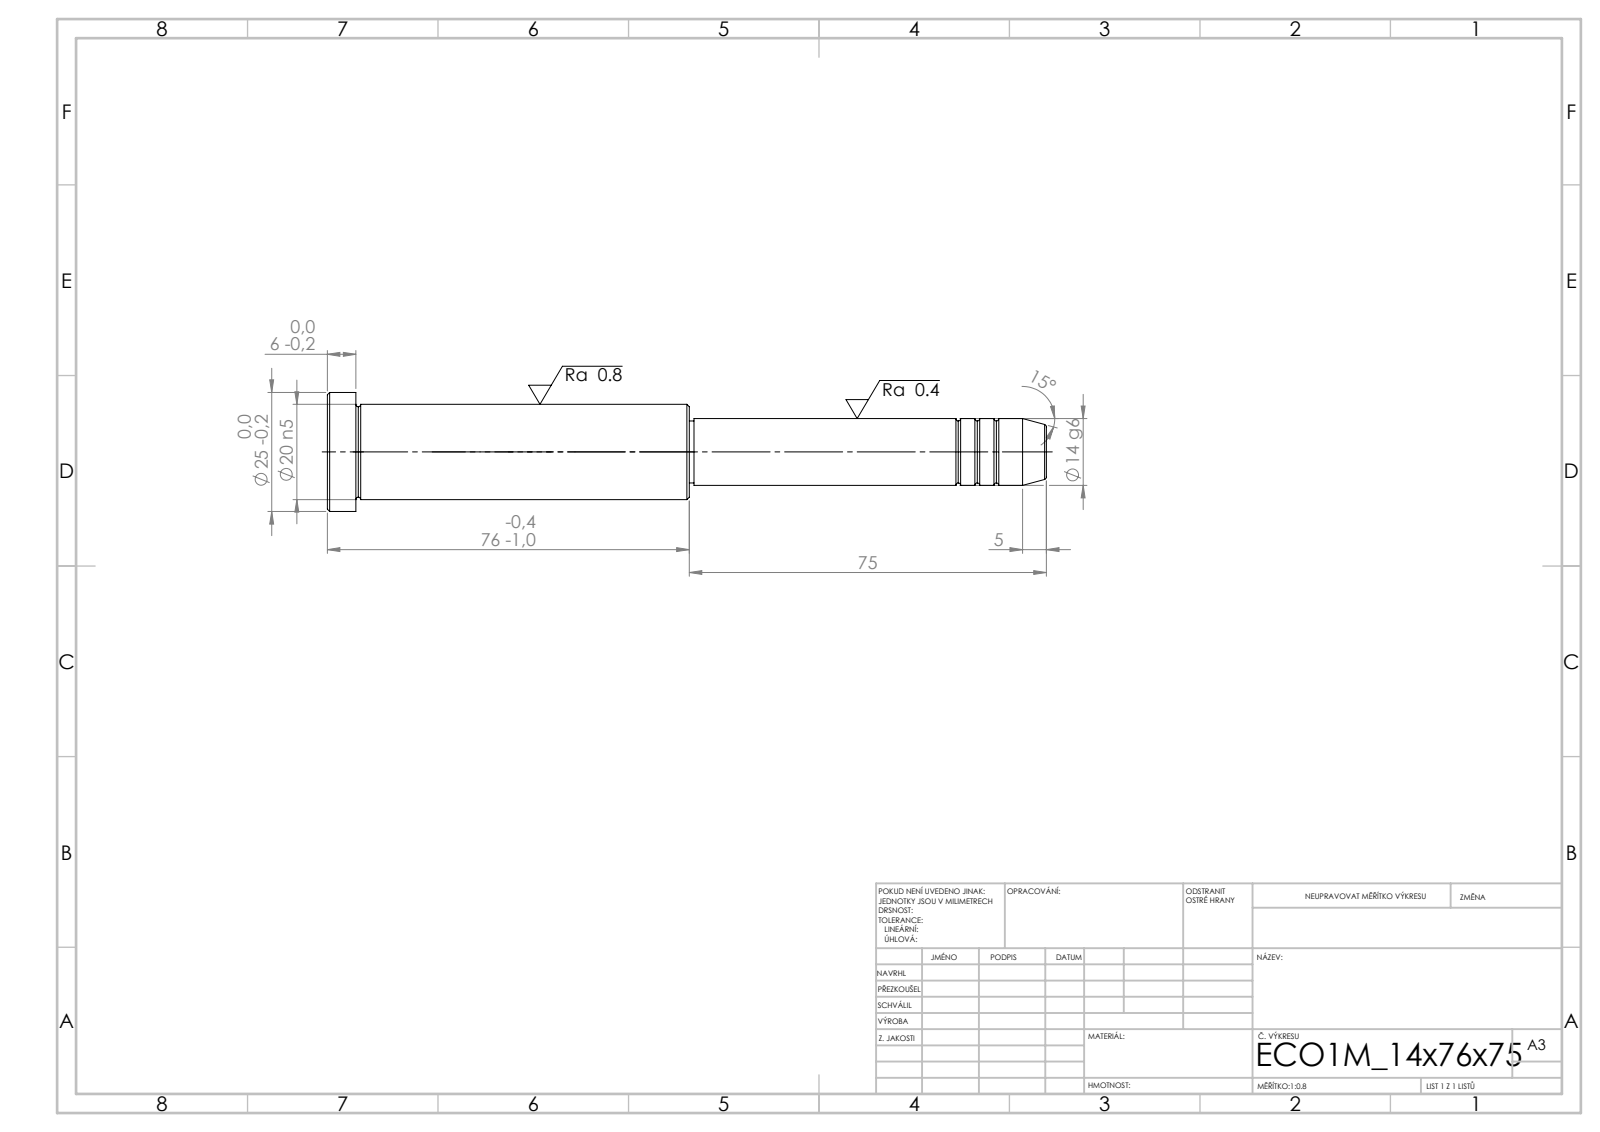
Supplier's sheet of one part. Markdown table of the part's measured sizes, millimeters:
| quantity | value |
| --- | --- |
| STEP written by | SolidWorks 2019 (CONFIG_CONTROL_DESIGN) |
| units | millimeters |
| bodies | 1 solid, 43 faces (5 planar, 14 cylindrical, 24 other) |
| overall size | 151 × 25 × 25 |
| volume | 36 230 mm³ |
| surface area | 9 174 mm² |
| round bosses / shafts (diameter × count) | 25 × 1, 20 × 1, 14 × 1, 13 × 1 |
| main face-to-face distances | 6, 70, 76, 75, 145, 151, 74, 1, 71, 77 |
